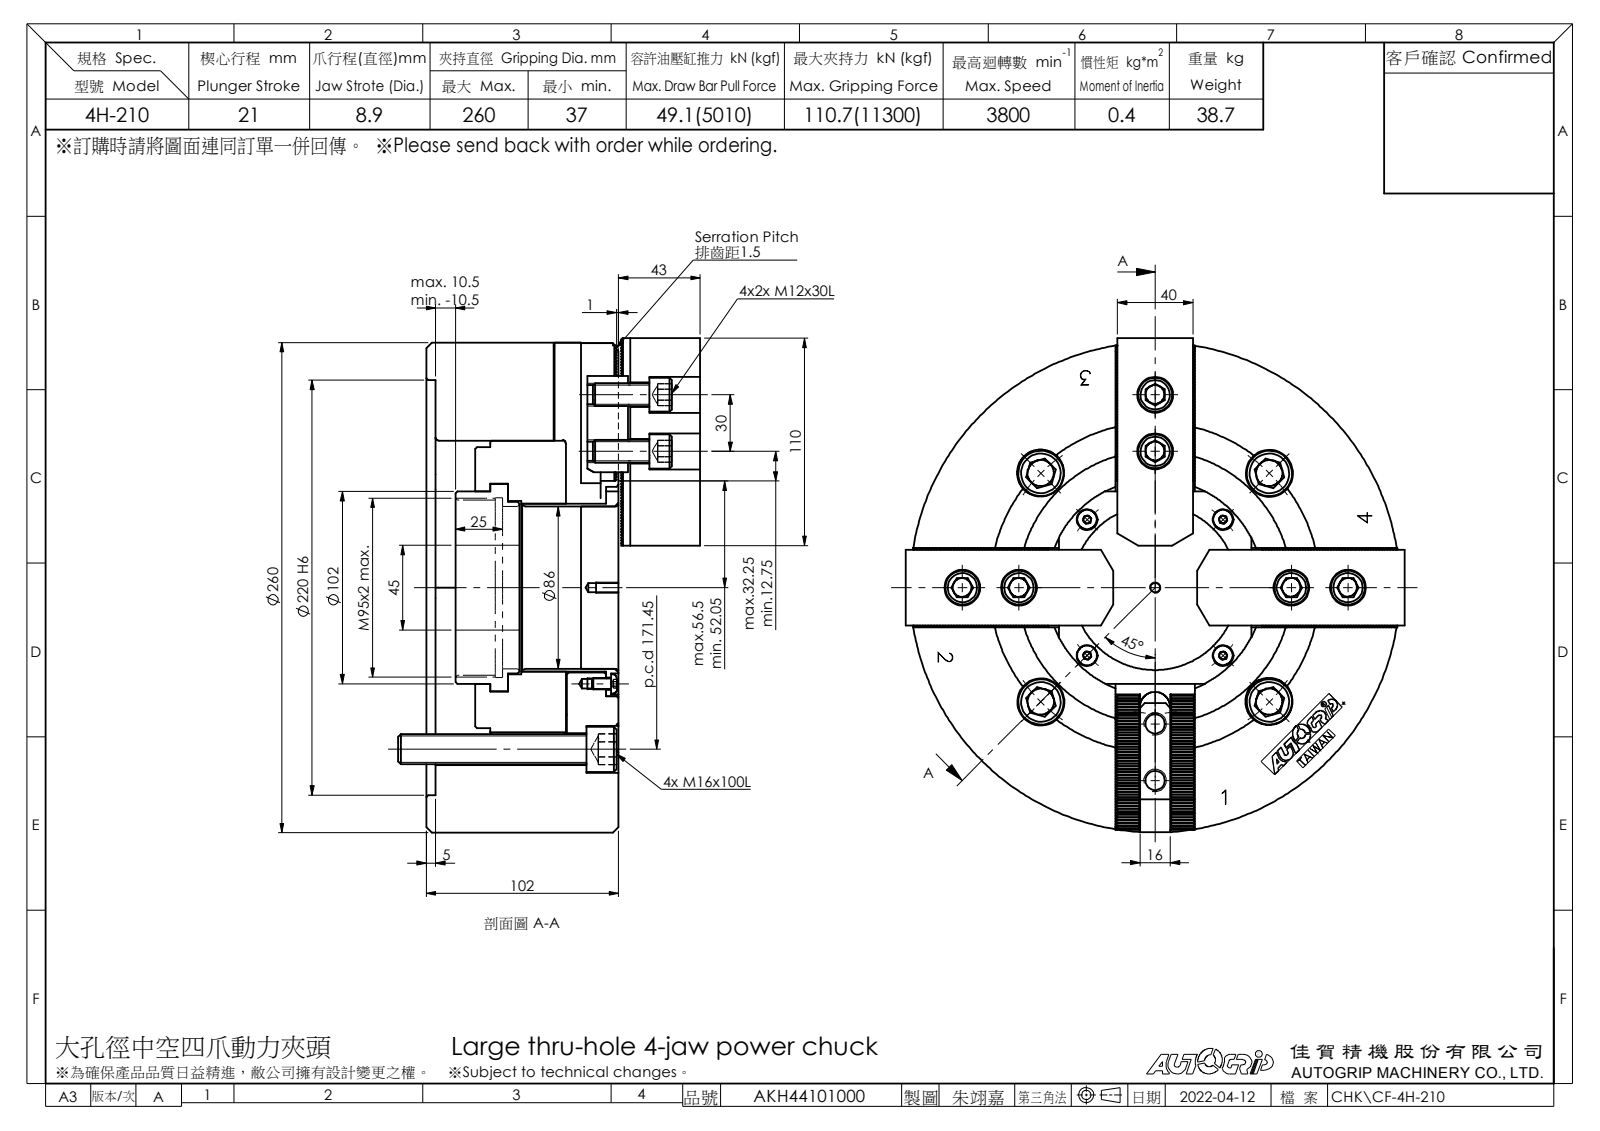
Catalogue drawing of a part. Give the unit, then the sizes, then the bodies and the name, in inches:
Units: inches
Overall size (bounding box): 10.413 × 10.413 × 6.311
Round holes (diameter × count): ⌀0.402 ×8, ⌀0.512 ×8, ⌀0.748 ×8, ⌀0.197 ×5, ⌀0.26 ×4, ⌀0.433 ×4, ⌀0.669 ×4, ⌀0.984 ×4, ⌀0.268 ×3, ⌀3.386 ×1, ⌀3.504 ×1, ⌀3.622 ×1
Round bosses / shafts (diameter × count): ⌀0.709 ×8, ⌀0.472 ×8, ⌀0.945 ×4, ⌀0.63 ×4, ⌀0.413 ×4, ⌀0.236 ×4, ⌀10.236 ×1, ⌀5.866 ×1
Partial cylindrical surfaces — rounded edges, fillets, slot ends (radius × count): R0.004 ×492, R0.315 ×4, R0.354 ×4, R5.315 ×4, R1.772 ×1, R2.264 ×1
Main face-to-face distances: 1.654, 0.039, 1.614, 1.102, 1.142, 0.512, 0.472, 1.339, 1.575, 1.083
Hole centre spacings: 2.011, 2.43, 2.895, 2.968, 3.926, 4.494, 4.929, 5.627
Volume: 311.9 in³ · Surface area: 991.6 in²
Bodies: 33 solids, 4984 faces (3587 planar, 1210 cylindrical, 187 other)
Part name (STEP PRODUCT): SJ-10; 半圓頭六角孔螺栓_M6x10; 圓頭內六角螺栓_M12x30; CF-4H-210-04000 (+8 more)
STEP written by: SolidWorks 2016 (CONFIG_CONTROL_DESIGN)
